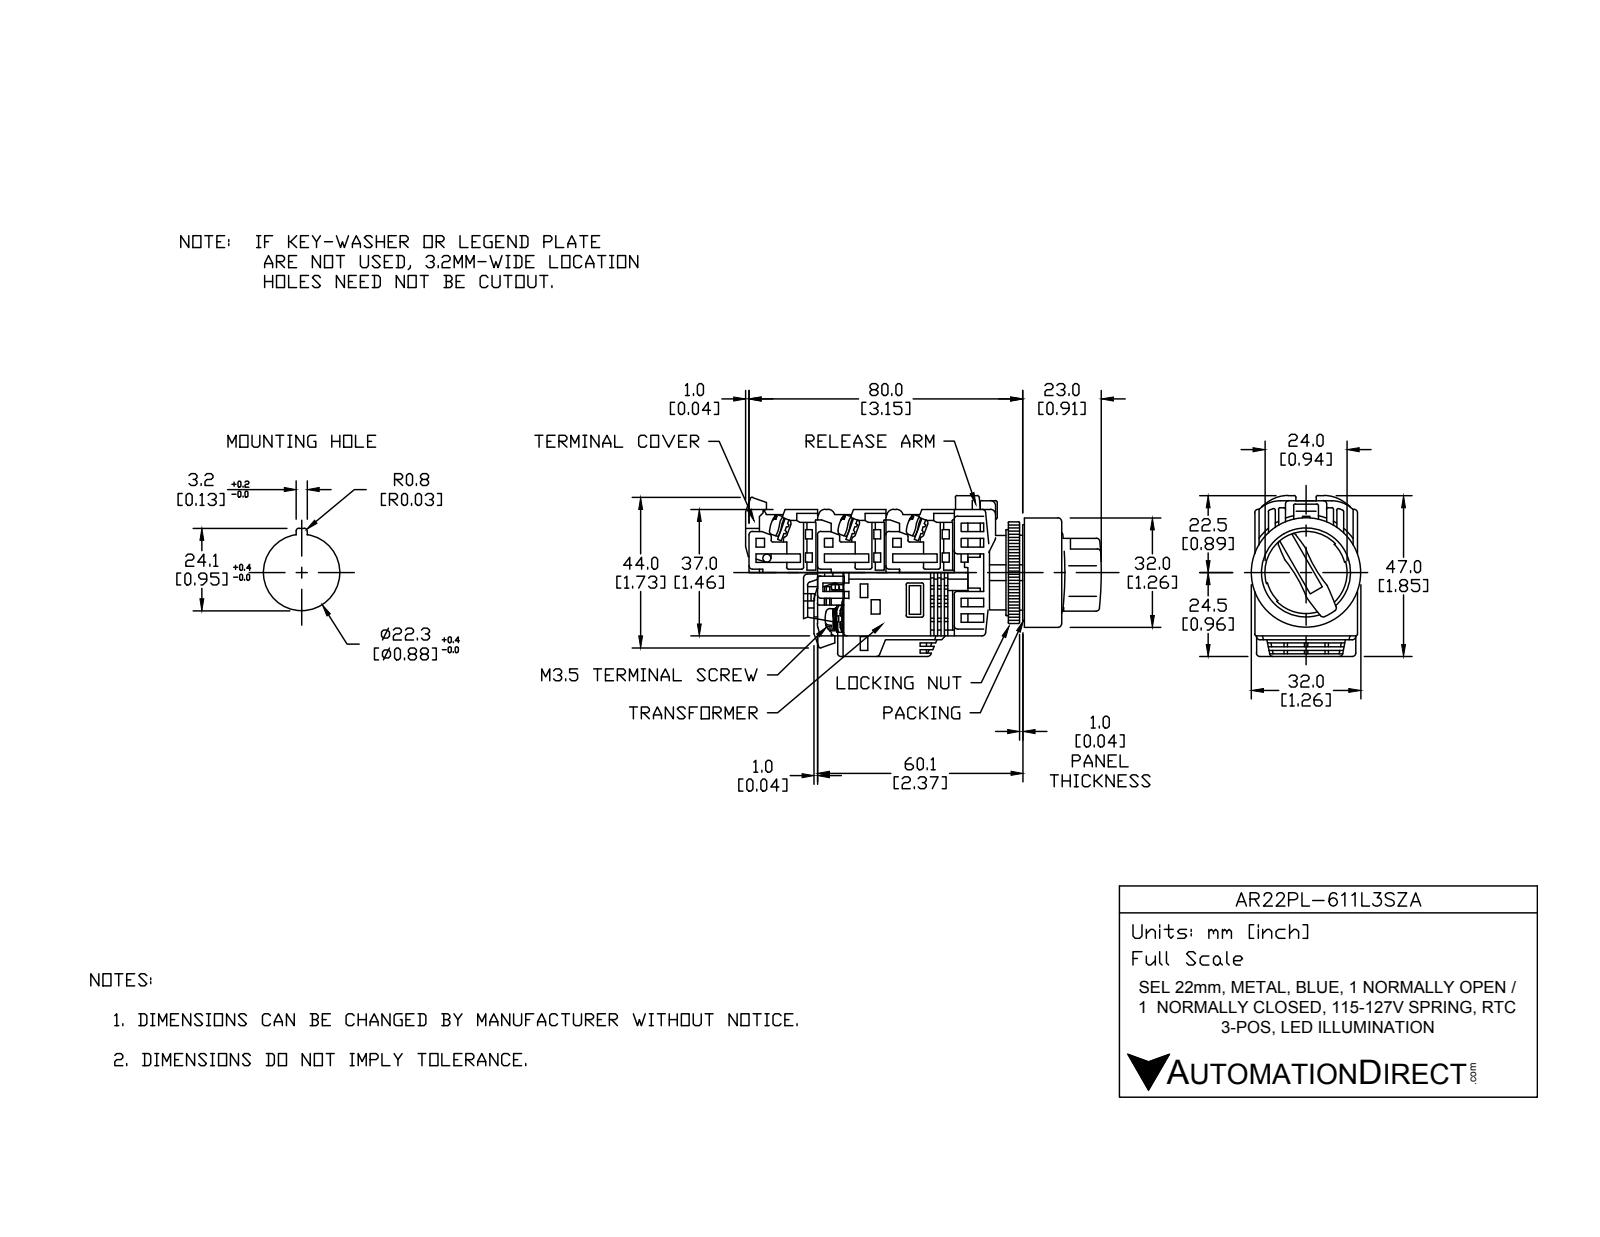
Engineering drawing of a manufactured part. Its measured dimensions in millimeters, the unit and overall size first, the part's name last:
Units: millimetres
Overall size (bounding box): 84.5 × 43.81 × 32
Round holes (diameter × count): ⌀21.8 ×1, ⌀22 ×1, ⌀25 ×1, ⌀31 ×1
Round bosses / shafts (diameter × count): ⌀5 ×6, ⌀32 ×1, ⌀30.5 ×1, ⌀29.8 ×1, ⌀24 ×1, ⌀21.75 ×1, ⌀17 ×1
Partial cylindrical surfaces — rounded edges, fillets, slot ends (radius × count): R0.5 ×48, R1.75 ×8, R1 ×6, R5 ×4, R4 ×2, R12 ×1, R16.59 ×1, R17.59 ×1
Main face-to-face distances: 1, 18, 20, 29, 3, 40, 28.5, 68.5, 2, 10
Volume: 57 503 mm³ · Surface area: 30 219 mm²
Bodies: 23 solids, 556 faces (386 planar, 139 cylindrical, 31 other)
Part name (STEP PRODUCT): AR22PL-611L3SZA
STEP written by: SolidWorks 2017 (AUTOMOTIVE_DESIGN)
